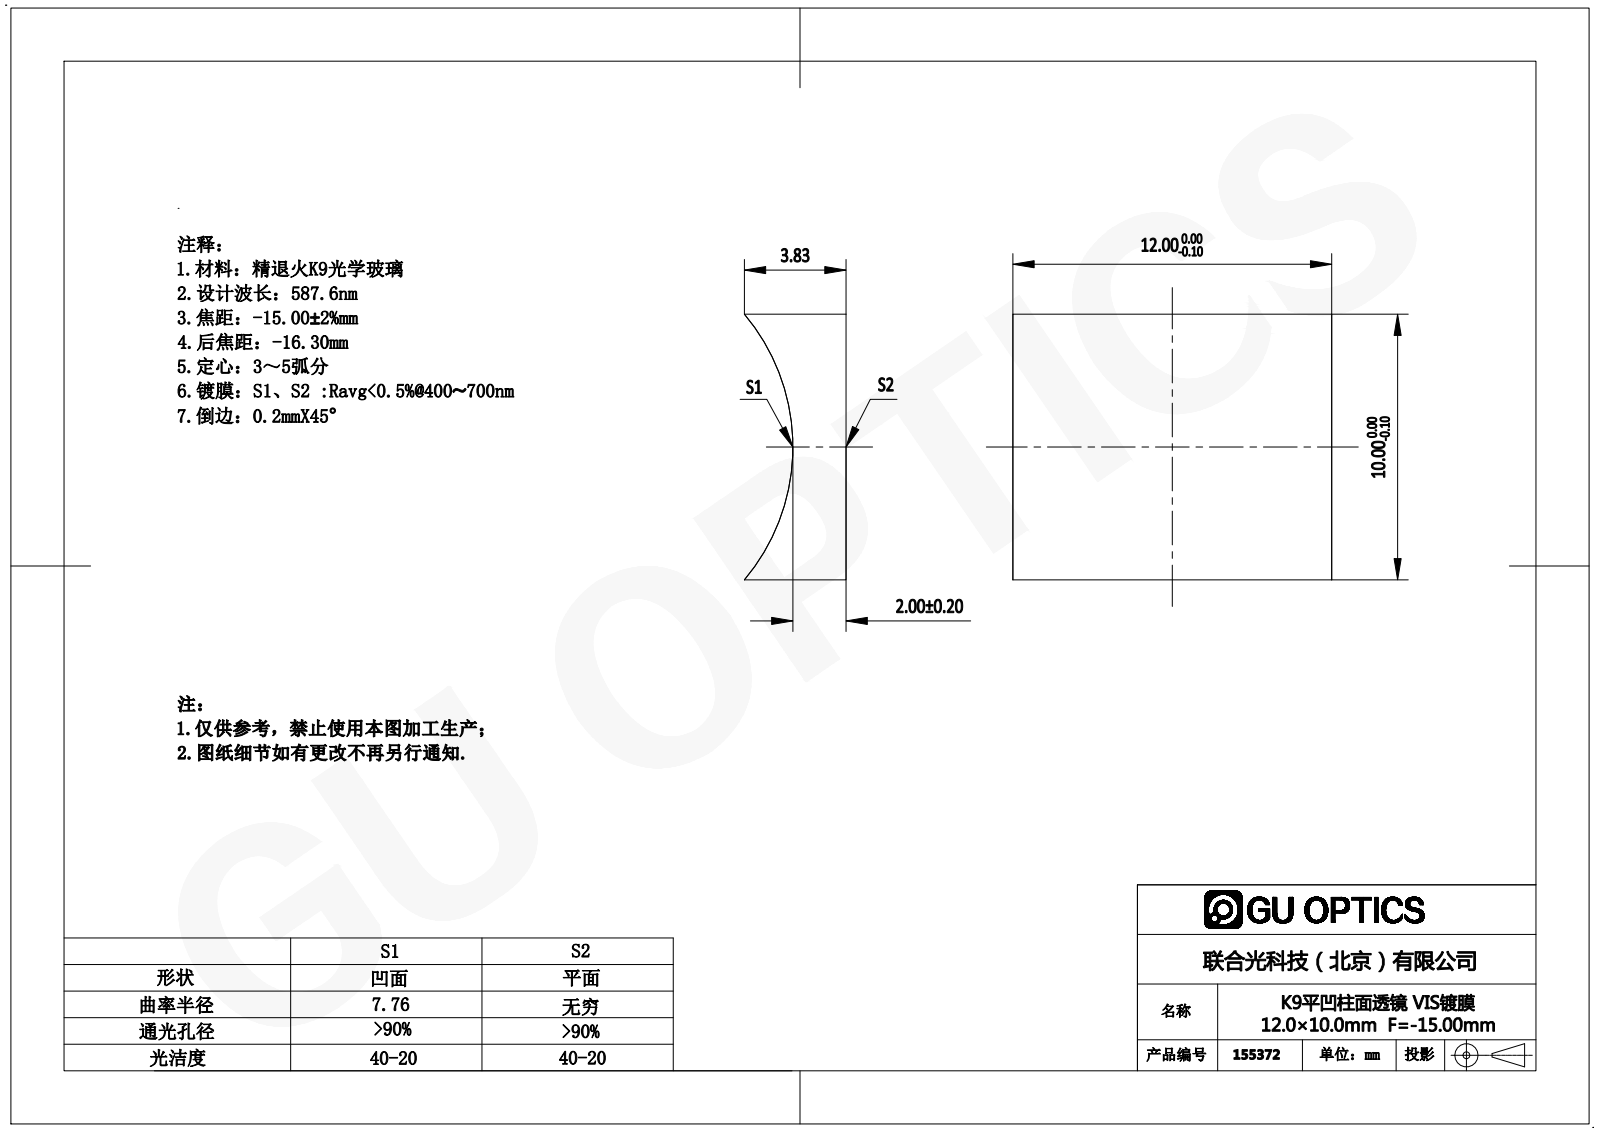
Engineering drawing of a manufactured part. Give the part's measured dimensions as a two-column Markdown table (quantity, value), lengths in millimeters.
| quantity | value |
| --- | --- |
| part name | 155339 |
| STEP written by | SolidWorks 2016 (AUTOMOTIVE_DESIGN) |
| units | millimeters |
| bodies | 1 solid, 6 faces (5 planar, 1 cylindrical, 0 other) |
| overall size | 12 × 10 × 3.83 |
| volume | 309 mm³ |
| surface area | 394 mm² |
| partial cylindrical surfaces (radius × count) | 7.76 × 1 |
| main face-to-face distances | 10, 12 |
